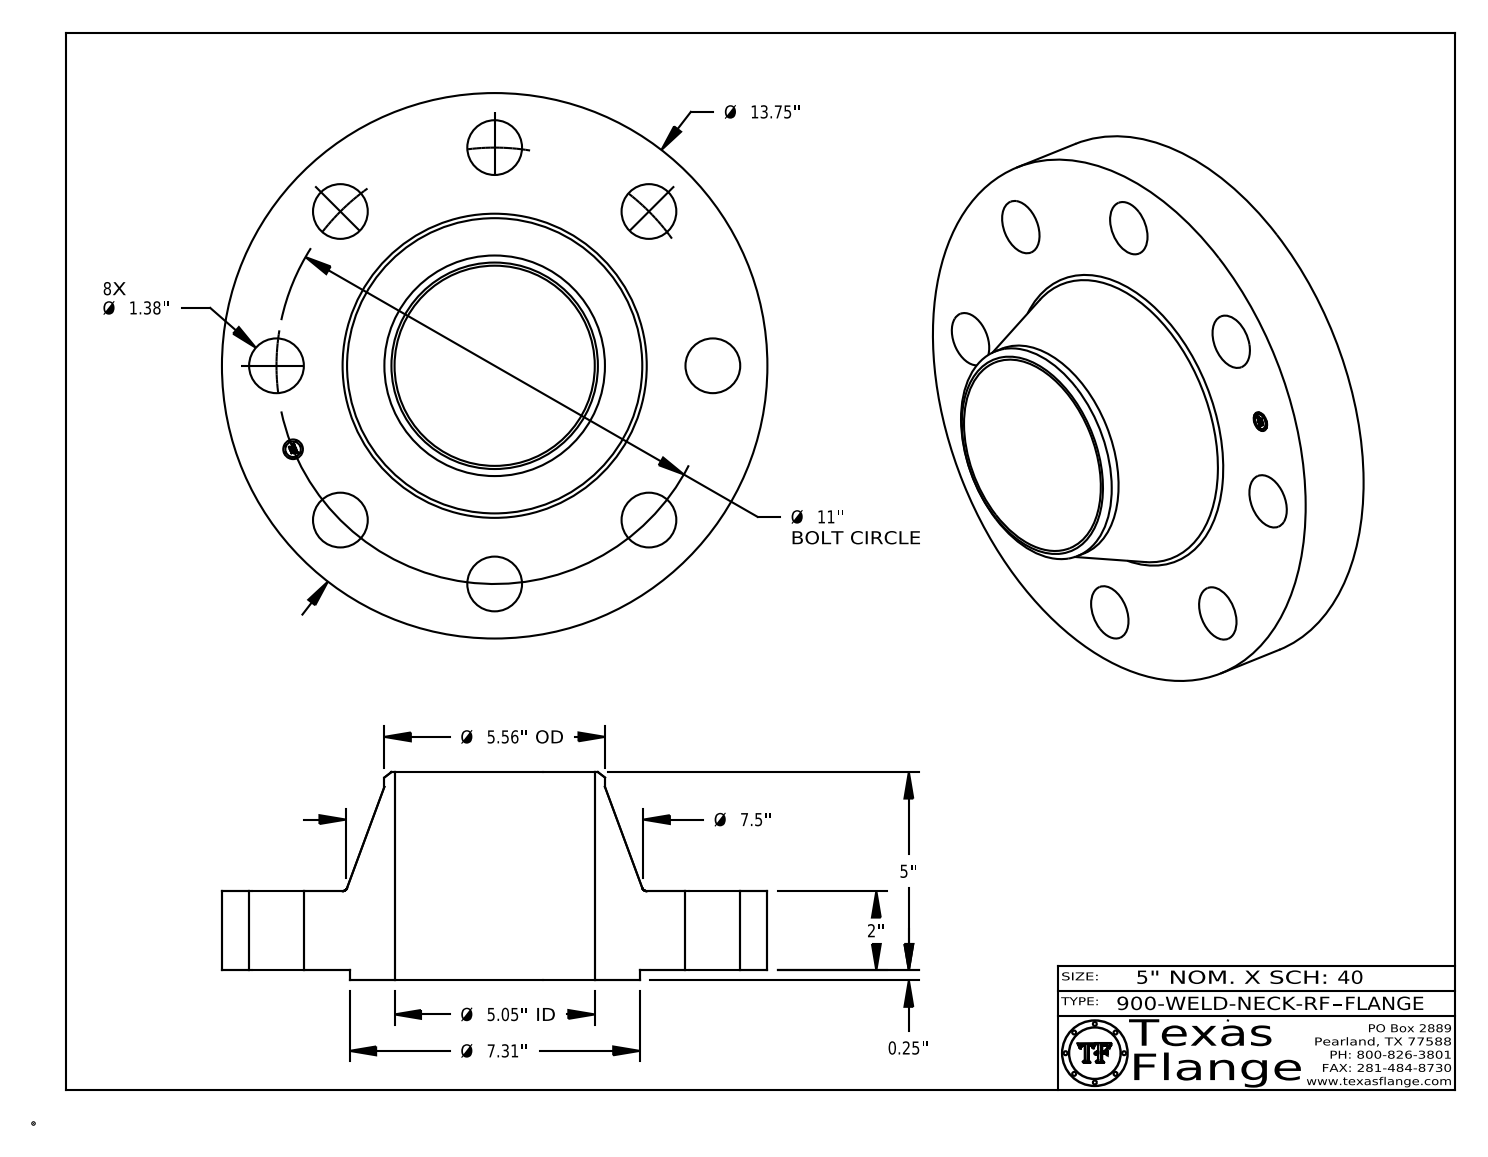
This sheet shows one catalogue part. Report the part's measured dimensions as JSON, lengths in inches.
{"part_name": "900-WELD-NECK-RF", "step_written_by": "CATIA V5 STEP AP214 (AUTOMOTIVE_DESIGN)", "units": "inches", "bodies": {"solids": 1, "faces": 419, "planar": 369, "cylindrical": 44, "other": 6}, "overall_size": [13.75, 13.75, 5.25], "volume_in3": 276, "surface_area_in2": 519.8, "round_holes": [[1.38, 8], [0.495, 1], [5.047, 1]], "round_bosses_or_shafts": [[0.03, 8], [13.75, 1], [7.31, 1], [5.56, 1], [0.39, 1]], "face_to_face_distances": [2, 0.25, 2.25, 5.25, 5, 3, 0.015, 2.235, 1.985, 3.015], "hole_center_spacings": [5.5, 4.209, 10.163, 7.778, 7.778, 2.146, 9.146, 11]}
